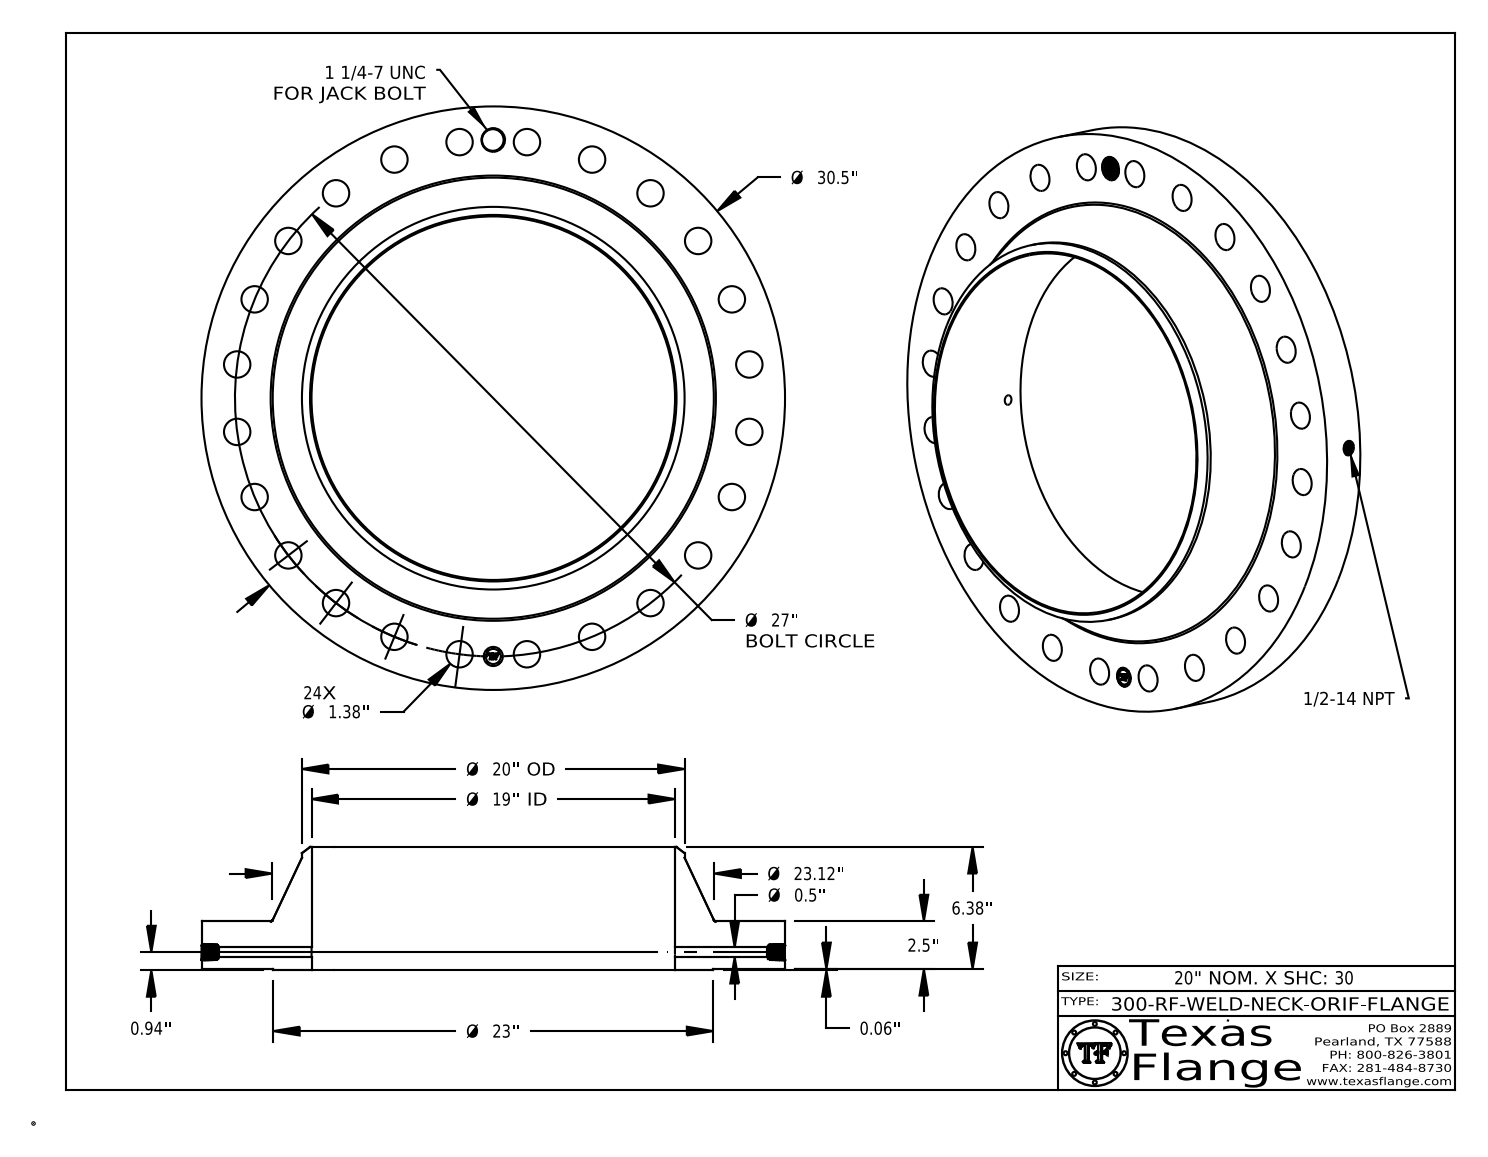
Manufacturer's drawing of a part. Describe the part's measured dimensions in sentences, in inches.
The part is named "300-RF-WELD-NECK". Its 3-D file was written by "CATIA V5 STEP AP214 (AUTOMOTIVE_DESIGN)". It is 1 solid with 818 faces: 369 planar, 131 cylindrical and 318 other. Overall it measures 30.5 by 30.5 by 6.44 inches. Its volume is 1 316 cubic inches and its surface area 1 906 square inches. Round holes: 24 of diameter 1.38, 1 of diameter 0.5, 1 of diameter 0.672, 1 of diameter 1, 1 of diameter 1.109, 1 of diameter 19. Round bosses or shafts: 8 of diameter 0.061, 1 of diameter 30.5, 1 of diameter 23, 1 of diameter 20, 1 of diameter 0.788. The main face-to-face distances are 2.5, 0.06, 2.56, 6.44, 6.38, 3.88, 2.545, 2.485, 0.015, 3.895. The hole center spacings are 13.5, 23.383, 24.945, 21.42, 3.524, 6.988, 19.092, 26.08.
